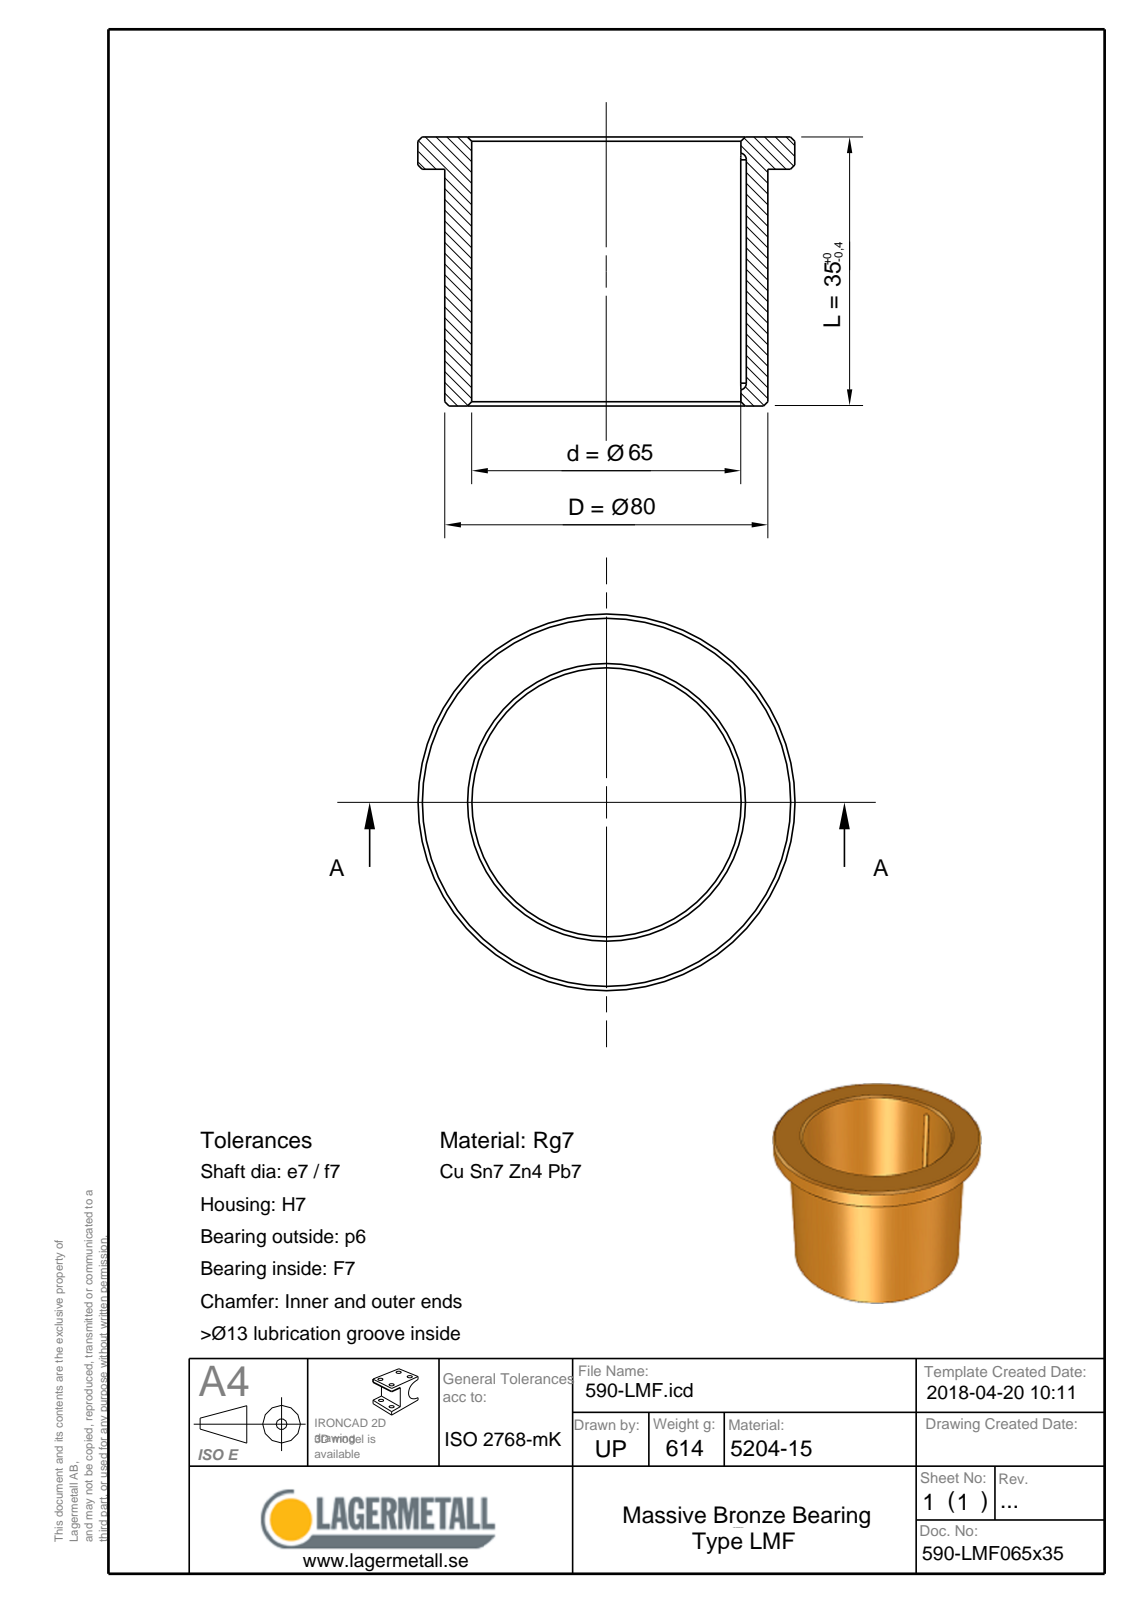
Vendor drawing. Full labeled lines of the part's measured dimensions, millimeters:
Part name (STEP PRODUCT): 590-LMF065x35
STEP written by: Spatial InterOp 3D (CONFIG_CONTROL_DESIGN)
Units: millimetres
Bodies: 1 solid, 16 faces (4 planar, 5 cylindrical, 7 other)
Overall size (bounding box): 90 × 90 × 35
Volume: 69 754 mm³ · Surface area: 21 608 mm²
Round holes (diameter × count): ⌀65 ×1
Round bosses / shafts (diameter × count): ⌀90 ×1, ⌀80 ×1
Partial cylindrical surfaces — rounded edges, fillets, slot ends (radius × count): R1.75 ×2
Main face-to-face distances: 35, 27, 8
